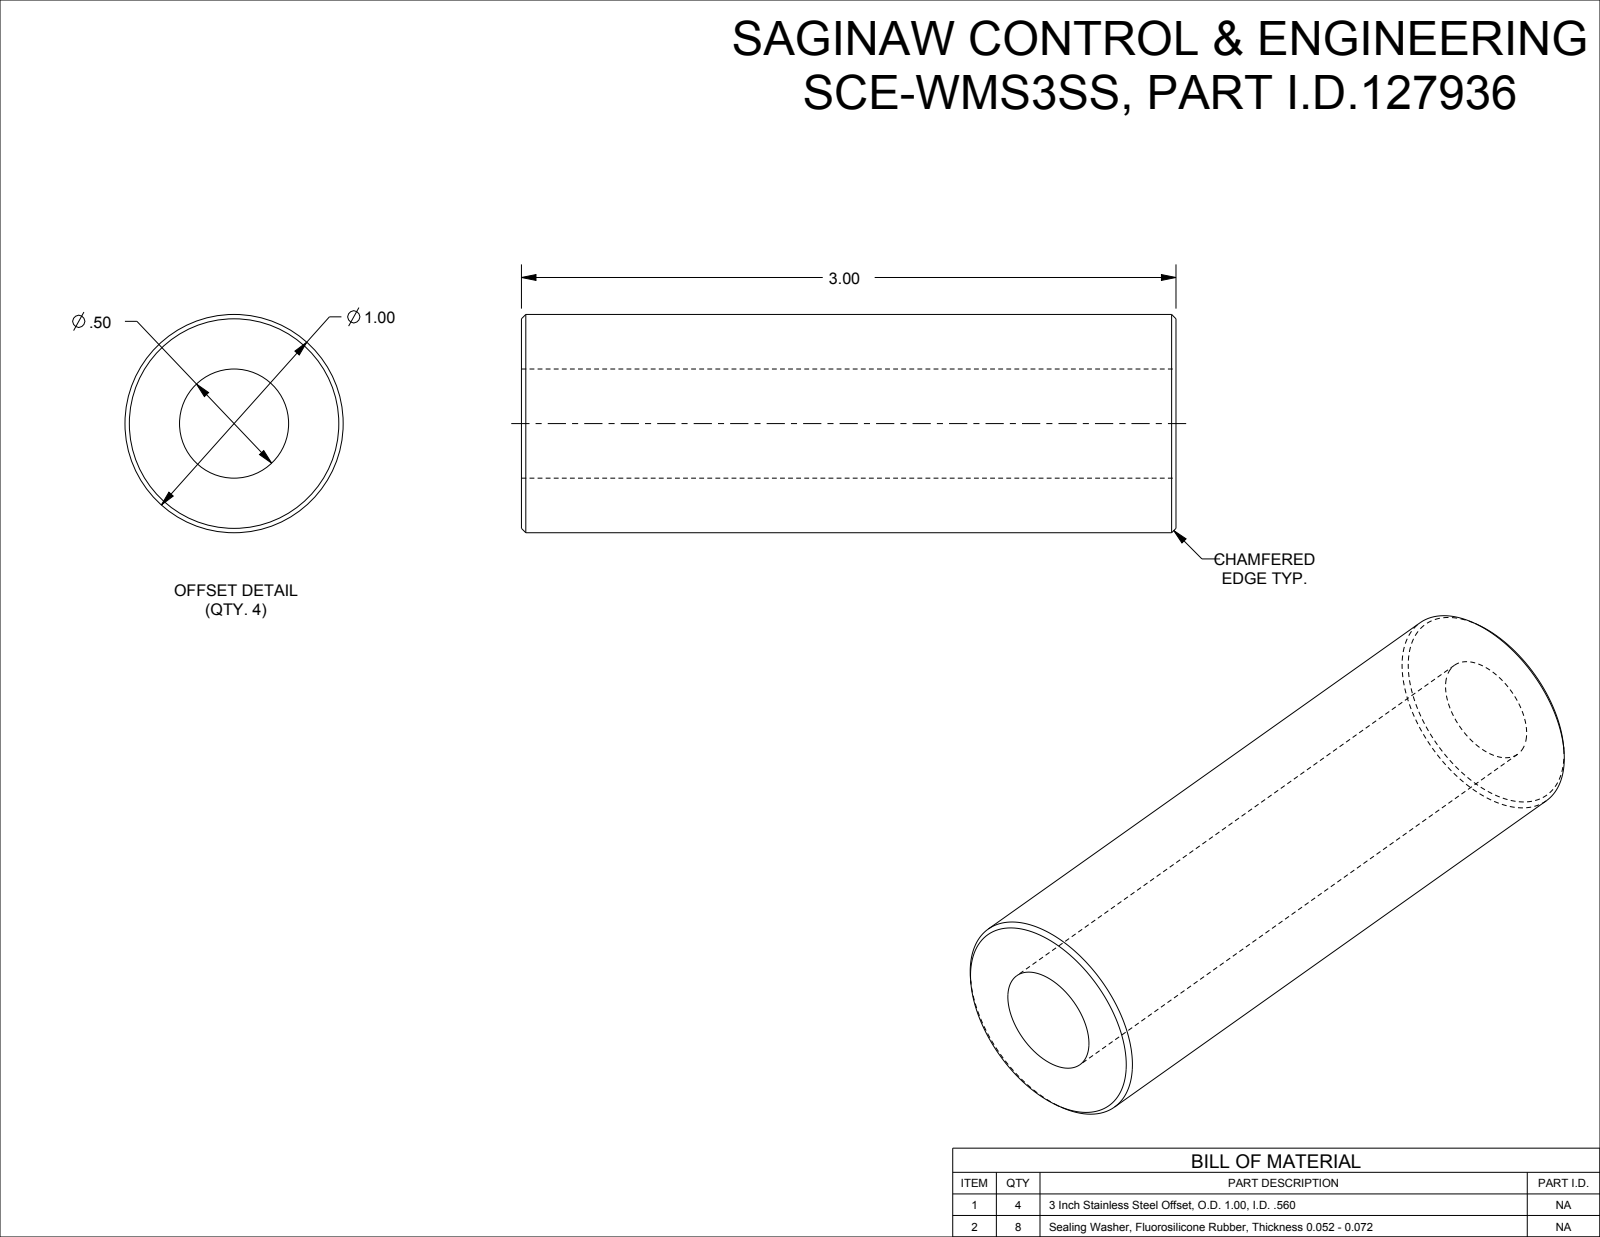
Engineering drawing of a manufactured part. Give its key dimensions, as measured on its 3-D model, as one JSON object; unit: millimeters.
{"part_name": "SCE-WMS3SS", "step_written_by": "SolidWorks 2019 (CONFIG_CONTROL_DESIGN)", "units": "millimeters", "bodies": {"solids": 3, "faces": 14, "planar": 6, "cylindrical": 6, "other": 2}, "overall_size": [79.3, 25.4, 25.4], "volume_mm3": 29790, "surface_area_mm2": 11210, "round_holes": [[9, 1], [12.7, 1]], "round_bosses_or_shafts": [[25.4, 1], [20.6, 1]], "face_to_face_distances": [76.2, 1.6, 77.8, 79.3]}
